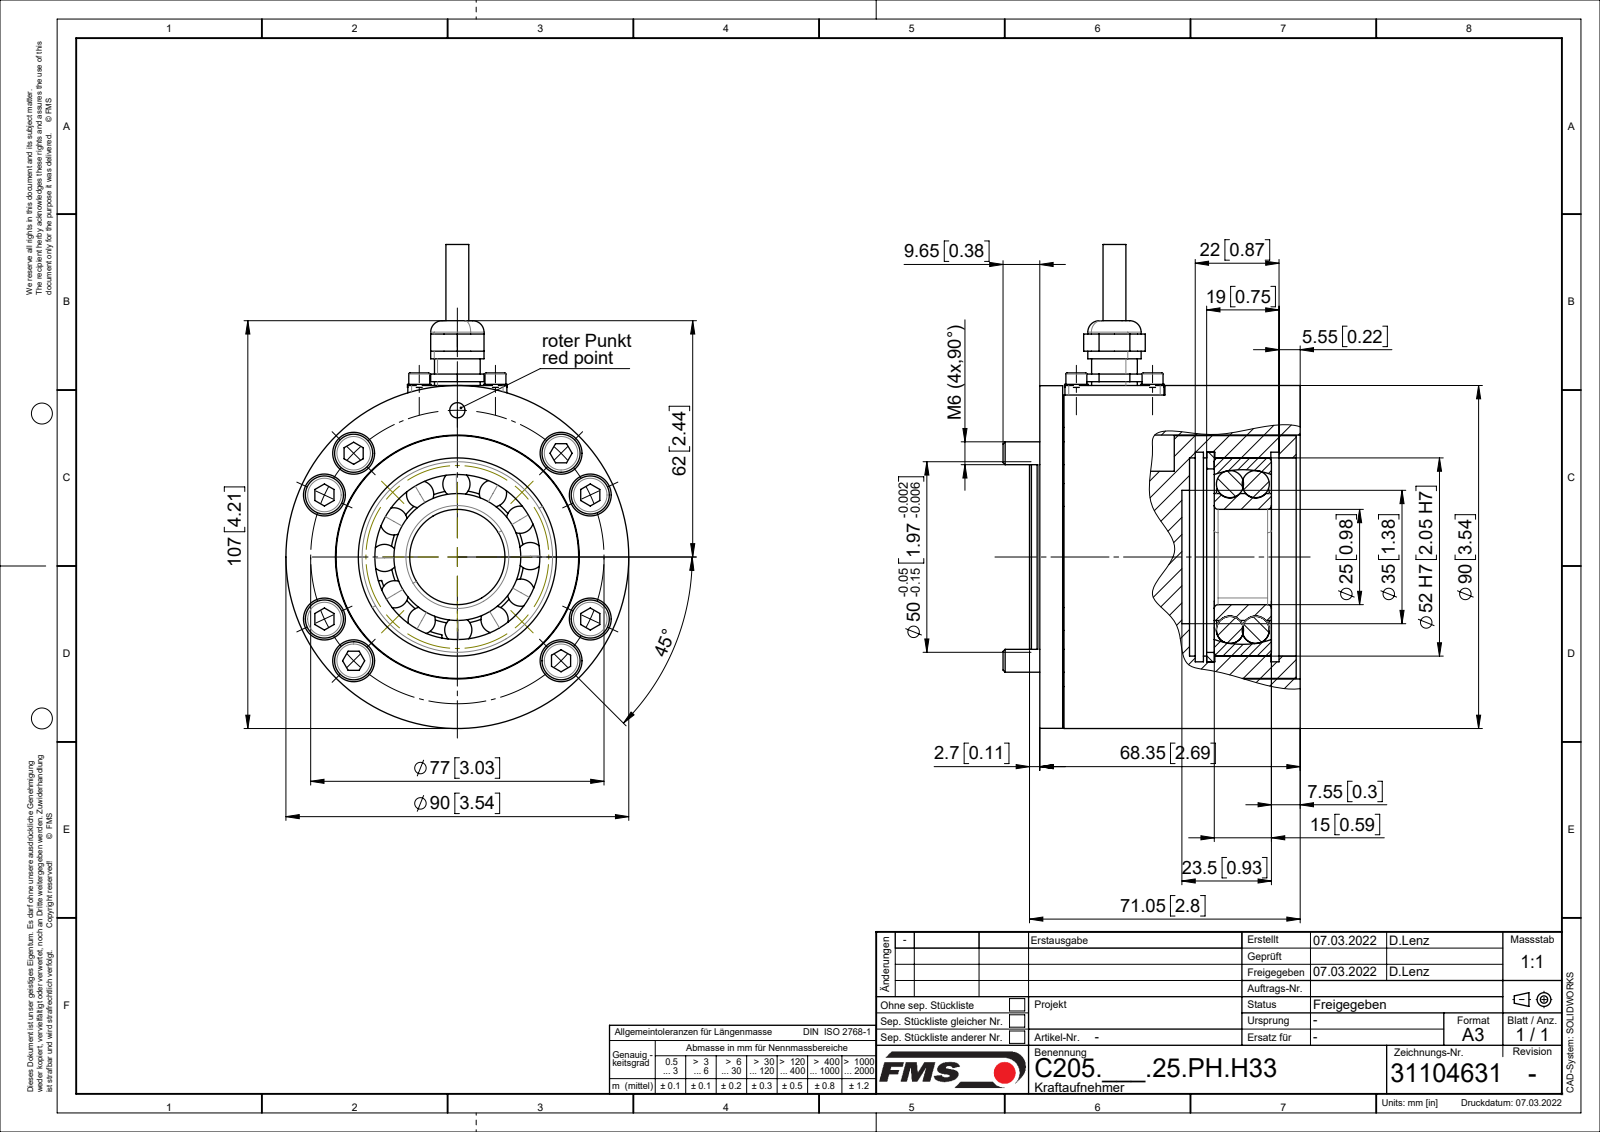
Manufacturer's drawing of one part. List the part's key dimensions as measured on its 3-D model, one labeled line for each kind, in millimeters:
Part name (STEP PRODUCT): Federringe_DIN127A_M03; 51283_01; 31101749_01; PKL_1205_01 (+8 more)
STEP written by: SolidWorks 2018 (CONFIG_CONTROL_DESIGN)
Units: millimetres
Bodies: 49 solids, 608 faces (222 planar, 234 cylindrical, 152 other)
Overall size (bounding box): 127 × 90 × 78
Volume: 298 818 mm³ · Surface area: 121 022 mm²
Round holes (diameter × count): ⌀6.5 ×8, ⌀11 ×8, ⌀2.5 ×6, ⌀3.1 ×4, ⌀3.4 ×4, ⌀5 ×4, ⌀7 ×4, ⌀4 ×2, ⌀6 ×1, ⌀10.2 ×1, ⌀12.2 ×1, ⌀18 ×1
Round bosses / shafts (diameter × count): ⌀10 ×8, ⌀6 ×8, ⌀6.2 ×4, ⌀5.5 ×4, ⌀3 ×4, ⌀90 ×1, ⌀89.9 ×1, ⌀63.7 ×1
Partial cylindrical surfaces — rounded edges, fillets, slot ends (radius × count): R0.1 ×4, R1 ×4, R4.24 ×2, R5 ×2, R20.8 ×1, R24.1 ×1
Main face-to-face distances: 6, 3.3, 2.7, 6.5, 32, 33.05, 2, 38, 29.3, 35.3
Hole centre spacings: 20, 38.5, 13.37, 14.14, 38.49, 44.16, 54.44, 63.07
